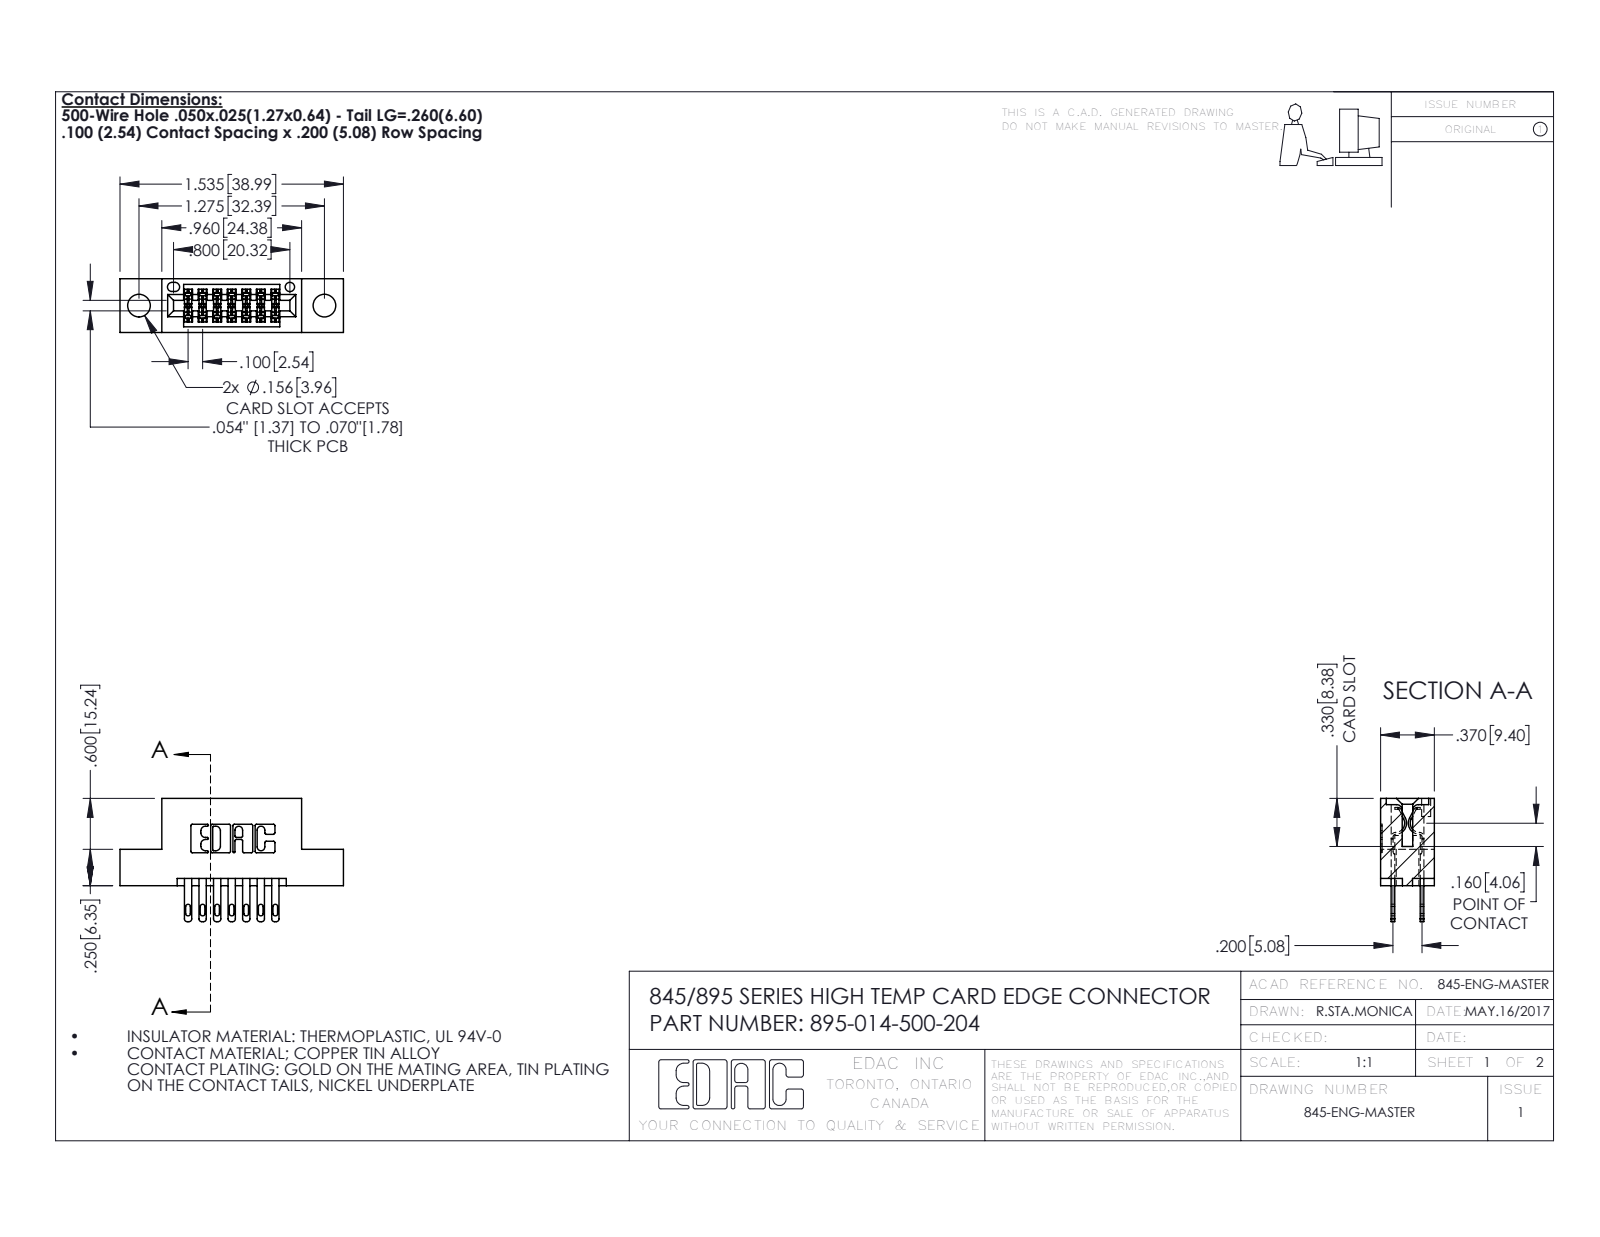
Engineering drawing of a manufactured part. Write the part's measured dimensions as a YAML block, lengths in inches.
part_name: "845 Part_Flush Mounting Lugs - 0.156 Dia-TH; 345-292-001_345-293-100; 895-014-500-204"
step_written_by: "SolidWorks 2020 (CONFIG_CONTROL_DESIGN)"
units: inches
bodies: {solids: 15, faces: 770, planar: 458, cylindrical: 312, other: 0}
overall_size: [1.535, 0.847, 0.37]
volume: 0.209
surface_area: 6.714
round_holes:
  - {diameter: 0.156, count: 2}
  - {diameter: 0.064, count: 1}
partial_cylinders:
  - {radius: 0.01, count: 22}
  - {radius: 0.006, count: 21}
  - {radius: 0.016, count: 14}
  - {radius: 0.02, count: 14}
  - {radius: 0.007, count: 6}
  - {radius: 0.031, count: 6}
  - {radius: 0.026, count: 3}
  - {radius: 0.014, count: 2}
face_to_face_distances: [0.2, 0.298, 0.072, 0.37, 0.1, 0.098, 0.272, 0.025, 0.225, 0.3]
hole_center_spacings: [0.27, 1.045, 1.275]
